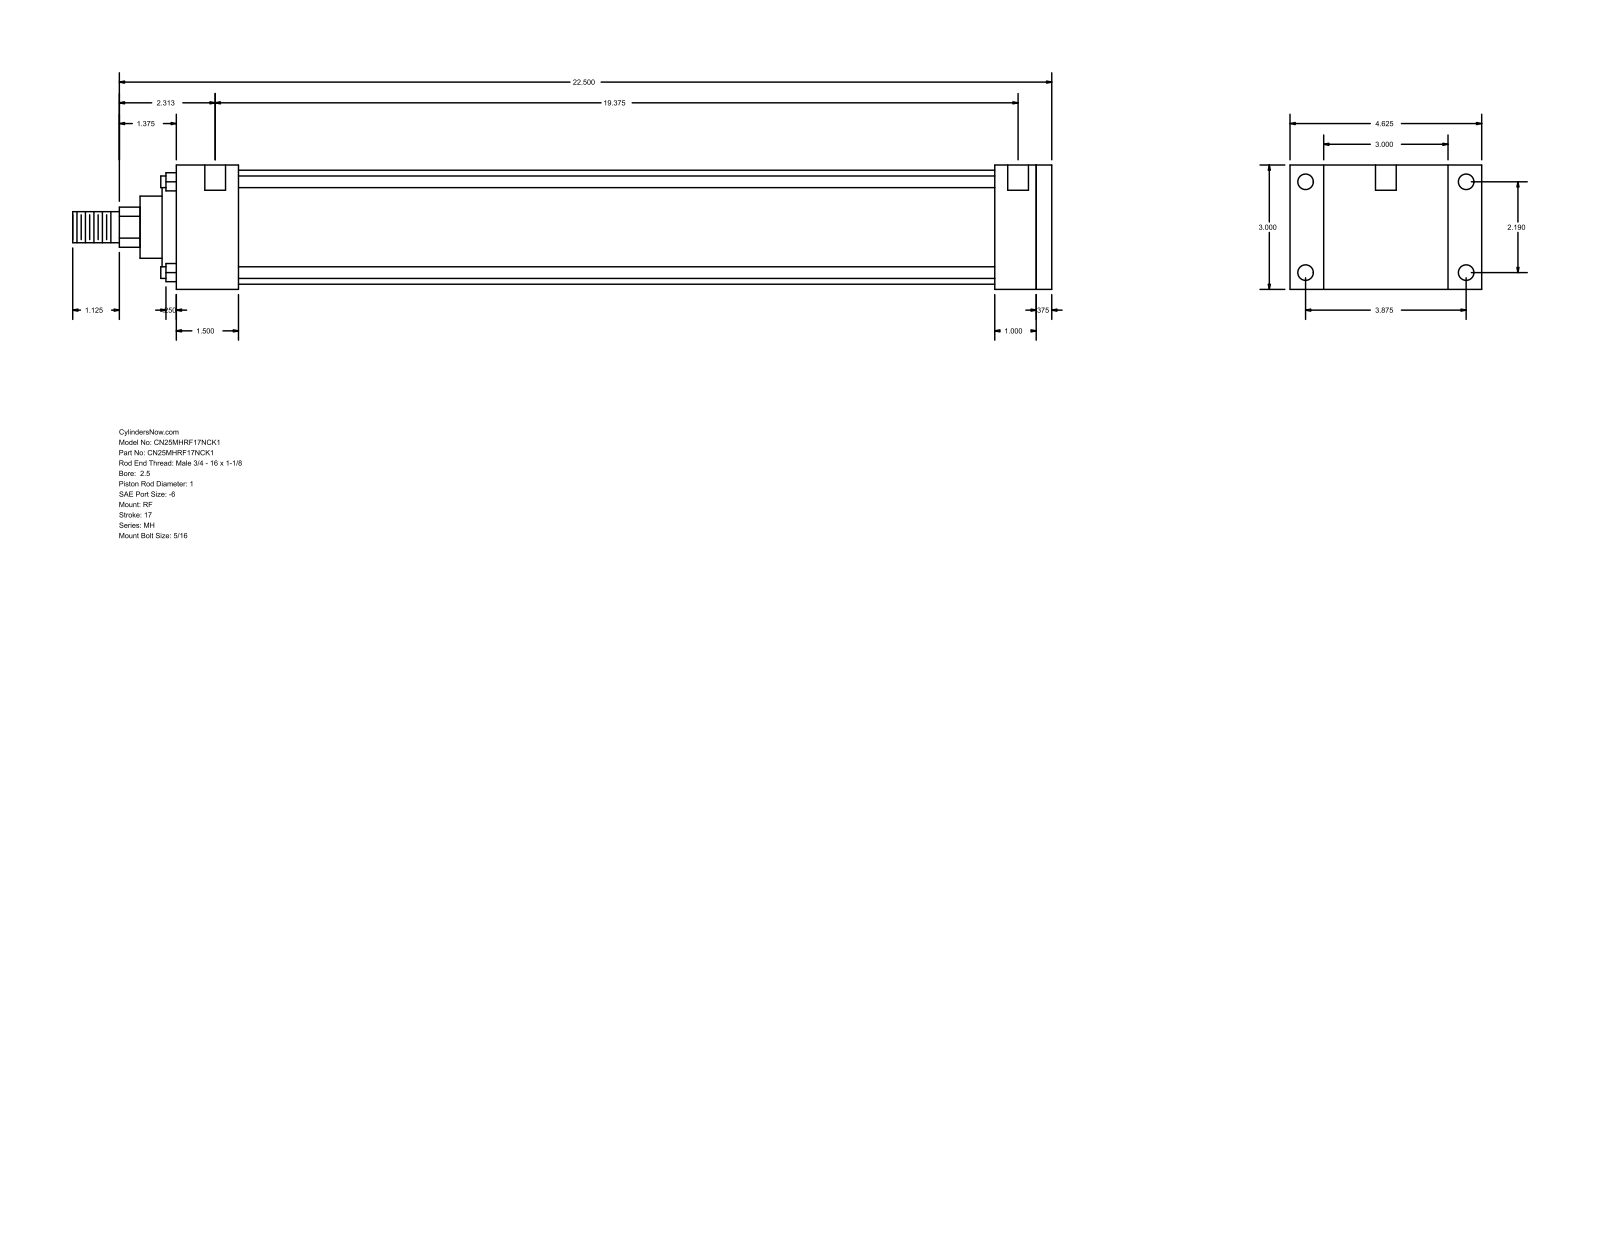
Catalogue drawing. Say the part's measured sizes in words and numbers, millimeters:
The part is named "MH_RF__0250_1". Its 3-D file was written by "GSSL Pune (CONFIG_CONTROL_DESIGN)". It is 0 solids with 94 faces: 65 planar, 29 cylindrical and 0 other. Overall it measures 600.08 by 117.47 by 76.2 millimeters. Round holes: 4 of diameter 5.56, 4 of diameter 9.53, 2 of diameter 12.7. Round bosses or shafts: 4 of diameter 7.14, 1 of diameter 69.85, 1 of diameter 60.33, 1 of diameter 38.1, 1 of diameter 25.4, 1 of diameter 19.05. Partial cylindrical surfaces (rounded edges, fillets, slot ends): 1 of radius 12.29. The main face-to-face distances are 76.2, 9.52, 536.58, 527.06, 25.4, 34.92, 501.66, 38.11, 463.55, 488.95. The hole center spacings are 55.62, 98.42, 113.05, 500.06, 3.18, 4.76, 492.12, 495.3.
